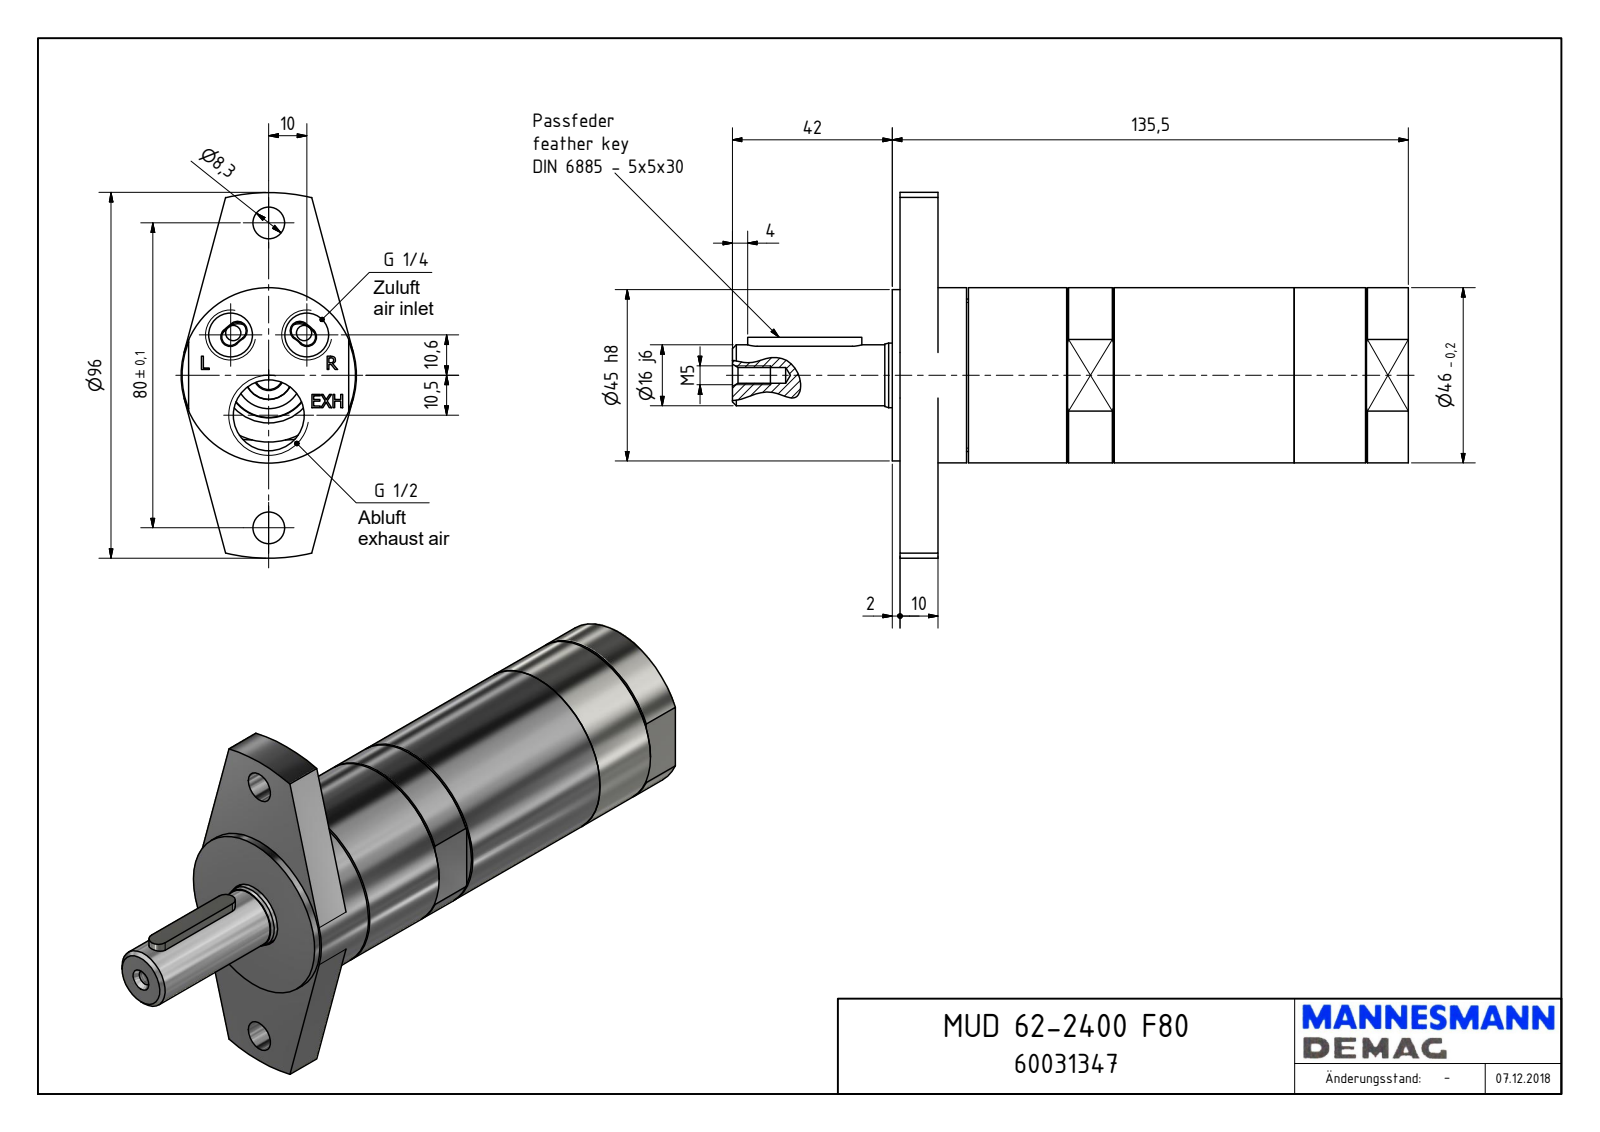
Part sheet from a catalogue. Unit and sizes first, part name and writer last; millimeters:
Units: millimetres
Overall size (bounding box): 177.5 × 96 × 46
Round holes (diameter × count): ⌀8.3 ×2, ⌀11.45 ×2, ⌀4.13 ×1, ⌀17.5 ×1, ⌀18.63 ×1, ⌀21.5 ×1, ⌀23 ×1
Round bosses / shafts (diameter × count): ⌀46 ×1, ⌀45 ×1, ⌀40 ×1, ⌀19.56 ×1, ⌀16.95 ×1, ⌀16 ×1
Partial cylindrical surfaces — rounded edges, fillets, slot ends (radius × count): R2.5 ×2, R5 ×2, R17.07 ×1, R19 ×1, R48 ×1
Main face-to-face distances: 10, 12, 2, 135.5, 133.5, 123.5, 42, 46, 8, 115.5
Hole centre spacings: 14.57, 23.35, 31.05, 40, 51.58, 10.5, 20, 29.5
Volume: 242 993 mm³ · Surface area: 34 176 mm²
Bodies: 1 solid, 164 faces (99 planar, 34 cylindrical, 31 other)
Part name (STEP PRODUCT): MUD 62-2400 F80_60031347
STEP written by: Autodesk Inventor 2018 (AUTOMOTIVE_DESIGN)
